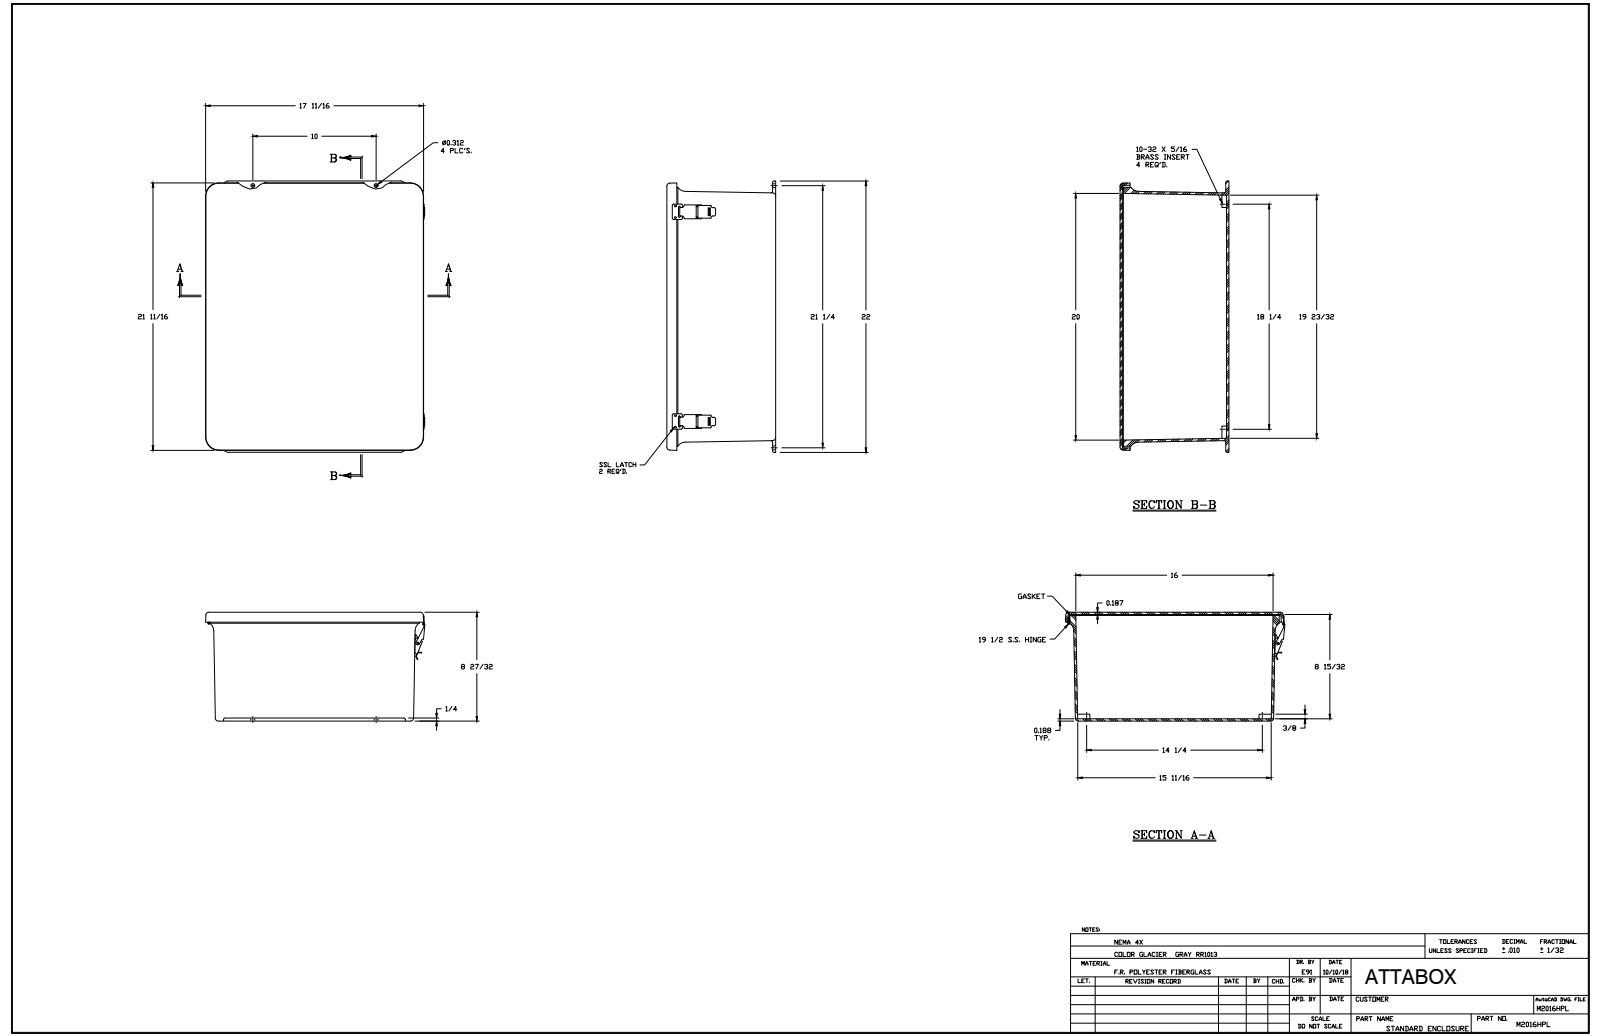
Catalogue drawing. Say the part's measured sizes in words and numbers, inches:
The part is named "M2016HPL". Its 3-D file was written by "SolidWorks 2018 (AUTOMOTIVE_DESIGN)". It is 42 solids with 1165 faces: 533 planar, 489 cylindrical and 143 other. Overall it measures 22 by 17.771 by 8.829 inches. Its volume is 283.6 cubic inches and its surface area 2 971 square inches. Round holes: 24 of diameter 0.14, 12 of diameter 0.131, 8 of diameter 0.104, 5 of diameter 0.152, 4 of diameter 0.13, 4 of diameter 0.156, 4 of diameter 0.218, 3 of diameter 0.135, 2 of diameter 0.375, 1 of diameter 0.085, 1 of diameter 0.135. Round bosses or shafts: 14 of diameter 0.125, 12 of diameter 0.25, 6 of diameter 0.125, 4 of diameter 0.27, 2 of diameter 0.3, 1 of diameter 0.17, 1 of diameter 0.155, 1 of diameter 0.155. Partial cylindrical surfaces (rounded edges, fillets, slot ends): 20 of radius 0.015, 20 of radius 0.031, 18 of radius 0.125, 16 of radius 0.045, 12 of radius 0.03, 8 of radius 0.023, 8 of radius 0.25, 6 of radius 0.06. The main face-to-face distances are 0.187, 8.642, 8.829, 0.188, 8.454, 8.641, 0.313, 0.5, 0.079, 8.563. The hole center spacings are 17, 3.75, 7.5, 0.25, 0.937, 17.017, 3.5, 4.
